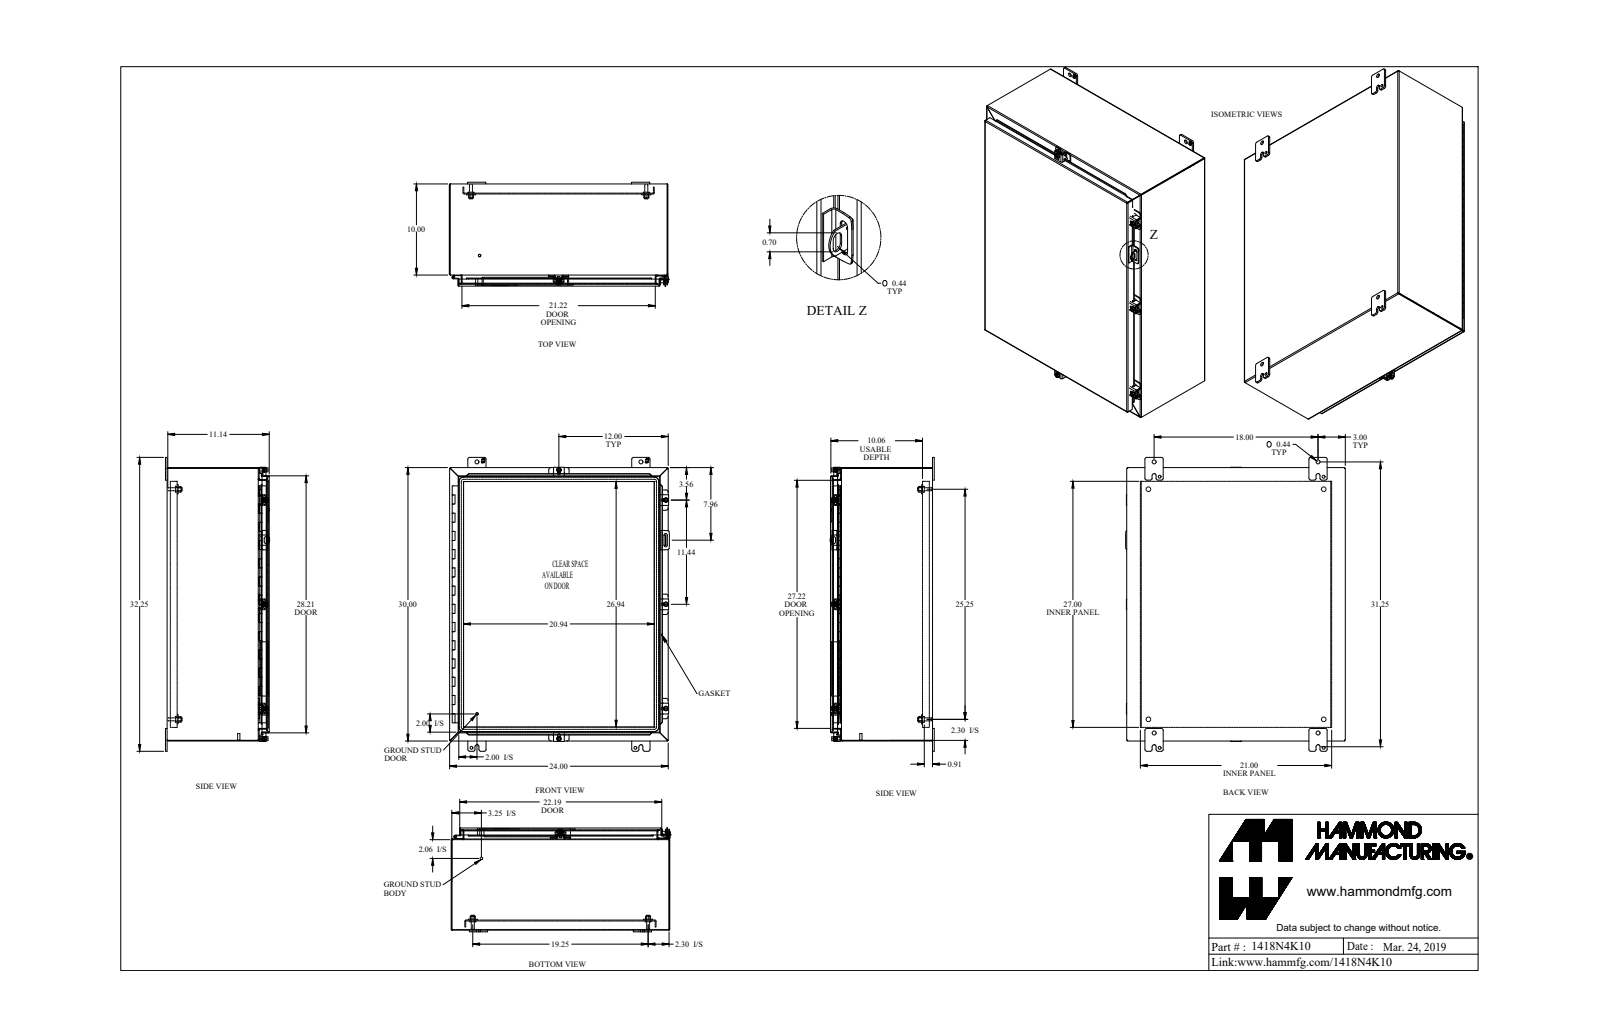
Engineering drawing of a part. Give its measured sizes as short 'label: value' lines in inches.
name: 1418N4K10_Default
written by: SolidWorks 2019 (CONFIG_CONTROL_DESIGN)
unit: in
bodies: 44 solids, 1603 faces (967 planar, 548 cylindrical, 88 other)
size: 32.25 × 24.126 × 11.437
volume: 274.8 in³; area: 7 209 in²
holes: 5× ⌀0.213, 5× ⌀0.265, 5× ⌀0.375, 4× ⌀0.313, 4× ⌀0.437, 4× ⌀0.5, 2× ⌀0.307, 2× ⌀0.445, 1× ⌀0.125, 1× ⌀0.187
bosses: 5× ⌀0.5, 5× ⌀0.39, 5× ⌀0.244, 4× ⌀0.65, 4× ⌀0.375, 4× ⌀0.33, 2× ⌀1, 2× ⌀0.281
rounds: 27× R0.048, 27× R0.143, 26× R0.188, 24× R0.036, 24× R0.108, 24× R0.25, 10× R0.125, 10× R0.141
face distances: 0.072, 0.072, 11.066, 11.138, 11.138, 11.21, 0.095, 23.928, 10.106, 10.034
hole spacings: 29.018, 1.736, 9.857, 18, 29.75, 34.772, 19.25, 25.25
